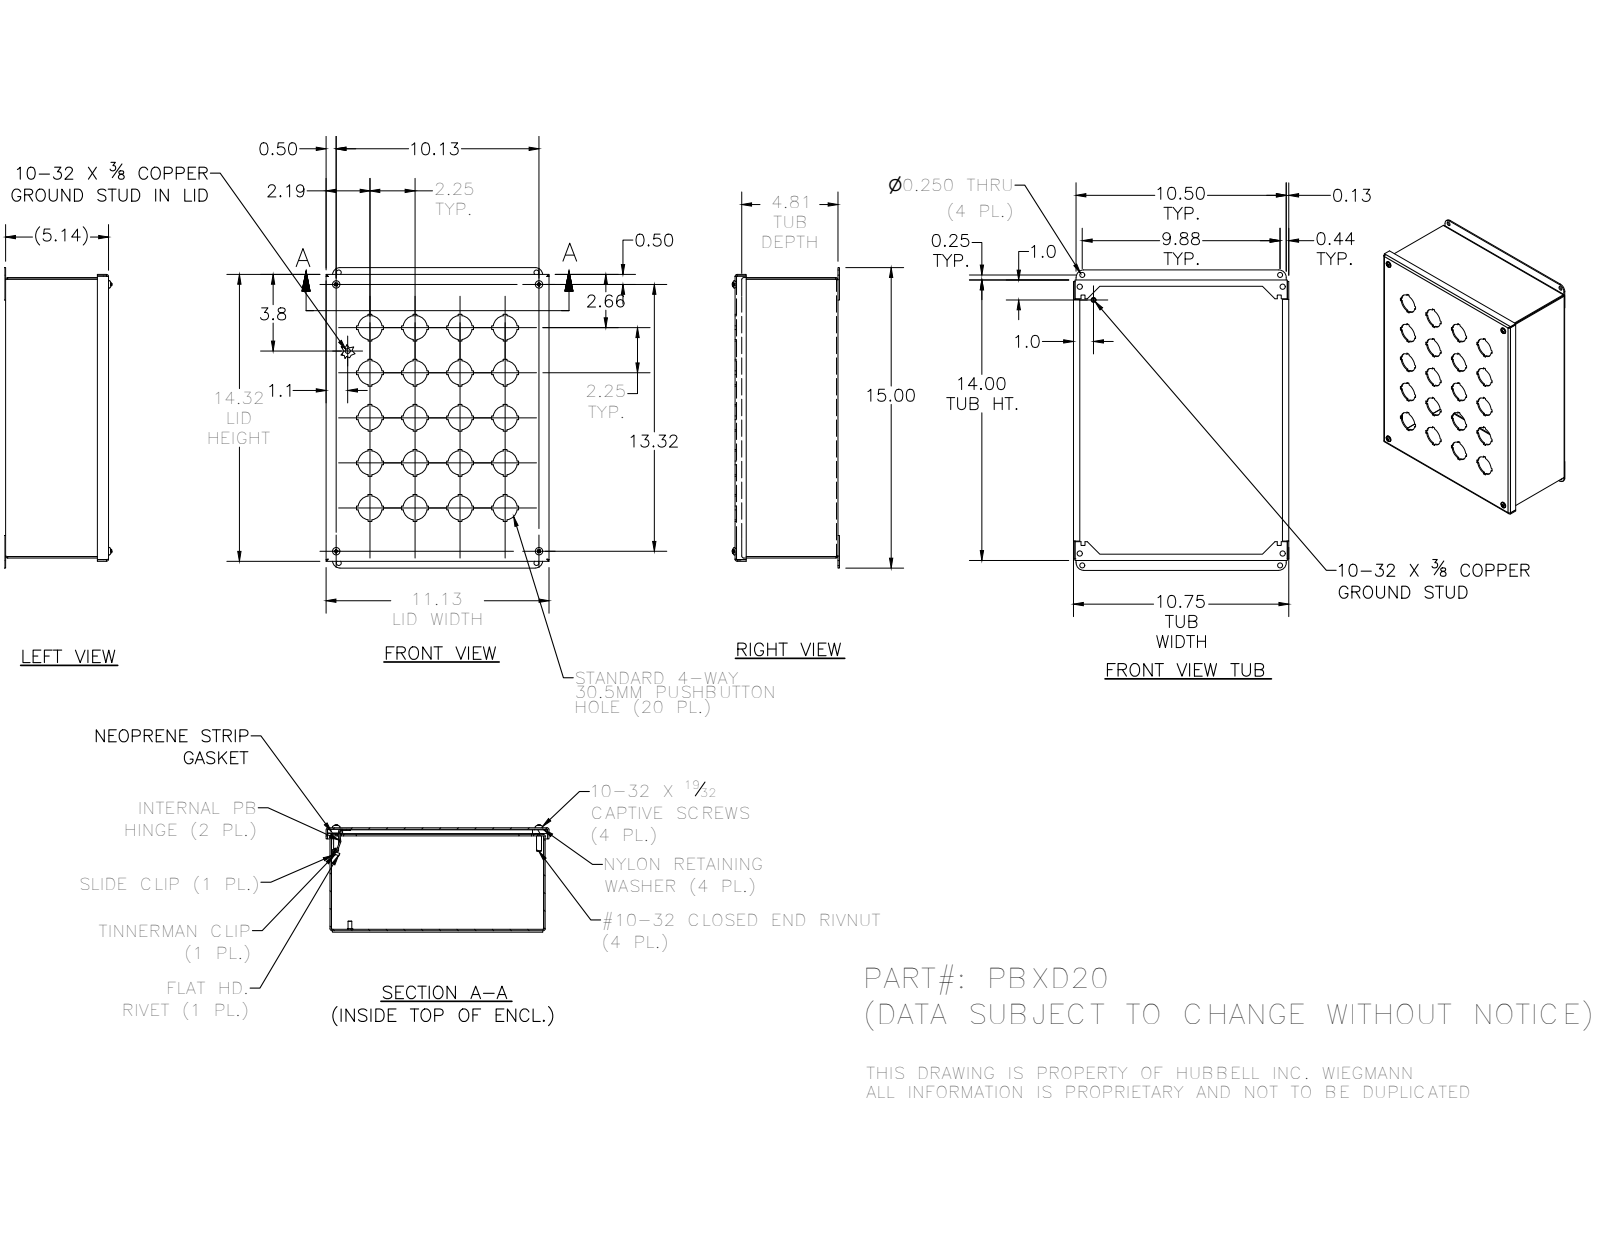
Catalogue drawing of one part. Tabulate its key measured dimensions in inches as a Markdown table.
| quantity | value |
| --- | --- |
| part name | PBXD20LID; 372163; 39077; PBXD20BKP (+8 more) |
| STEP written by | Autodesk Inventor 2016 (AUTOMOTIVE_DESIGN) |
| units | inches |
| bodies | 25 solids, 929 faces (603 planar, 212 cylindrical, 114 other) |
| overall size | 15 × 11.13 × 5.346 |
| volume | 50.57 in³ |
| surface area | 1 303 in² |
| round holes (diameter × count) | 1.2 × 20, 0.156 × 4, 0.196 × 4, 0.25 × 4, 0.257 × 4, 0.278 × 4, 0.281 × 4, 0.313 × 4, 0.14 × 2 |
| round bosses / shafts (diameter × count) | 0.19 × 6, 0.453 × 4, 0.406 × 4, 0.373 × 4, 0.248 × 4, 0.25 × 3, 0.125 × 1 |
| partial cylindrical surfaces (radius × count) | 0.031 × 12, 0.105 × 12, 0.188 × 6, 0.089 × 4, 0.09 × 4, 0.375 × 4, 0.031 × 3, 0.063 × 3 |
| main face-to-face distances | 0.074, 5.068, 5.142, 4.994, 10.676, 13.926, 10.602, 10.75, 13.852, 14 |
| hole center spacings | 5.031, 2.25, 3.182, 4.5, 7.115, 8.113, 6.75, 6.364 |
